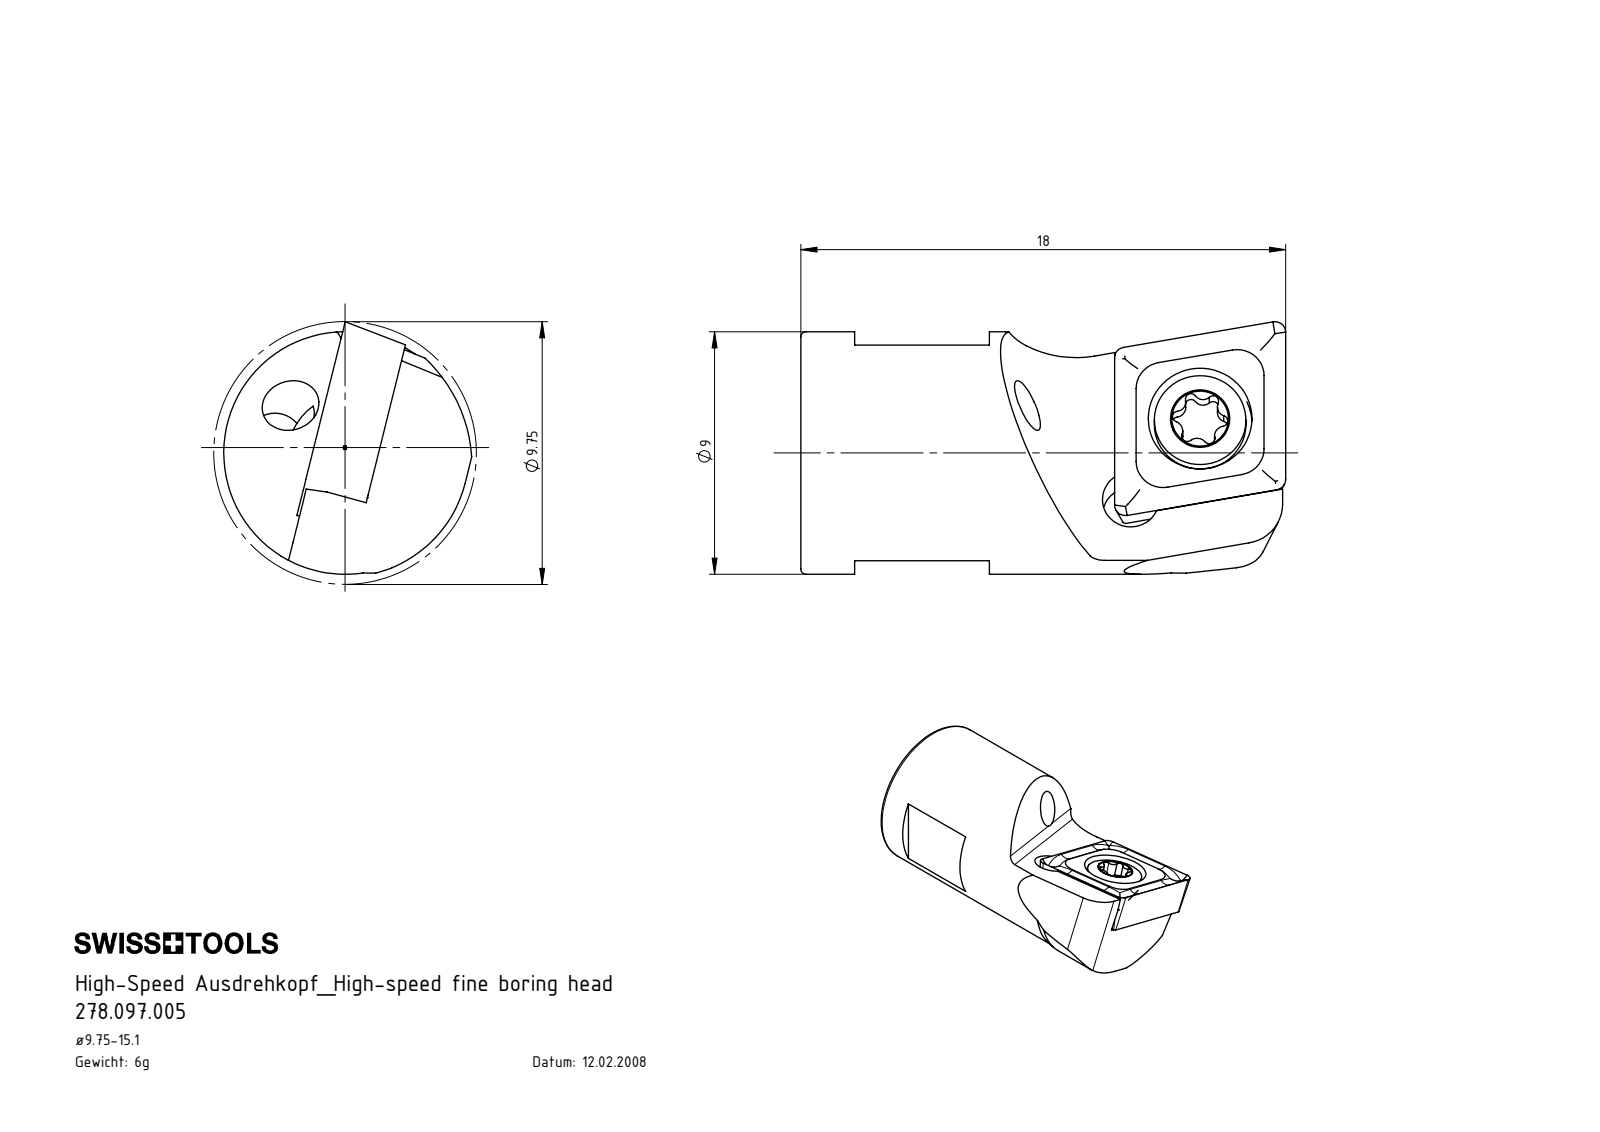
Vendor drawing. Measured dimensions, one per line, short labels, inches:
name: CCMT060204; WCA-ER2.001.005_B; HS5-A10.K11.018_D; HS5-A10.K11.018
written by: SolidWorks 2017 (CONFIG_CONTROL_DESIGN)
unit: in
bodies: 3 solids, 130 faces (40 planar, 39 cylindrical, 51 other)
size: 0.709 × 0.369 × 0.363
volume: 0.046 in³; area: 1.4 in²
holes: 1× ⌀0.079, 1× ⌀0.081, 1× ⌀0.083, 1× ⌀0.11, 1× ⌀0.152, 1× ⌀0.165
bosses: 1× ⌀0.354, 1× ⌀0.134, 1× ⌀0.098
rounds: 6× R0.008, 5× R0.014, 1× R0.014, 1× R0.02, 1× R0.059, 1× R0.157, 1× R0.181, 1× R0.217
face distances: 0.09, 0.315, 0.094, 0.463, 0.197, 0.079, 0.384, 0.276, 0.187, 0.058
hole spacings: 0.158
